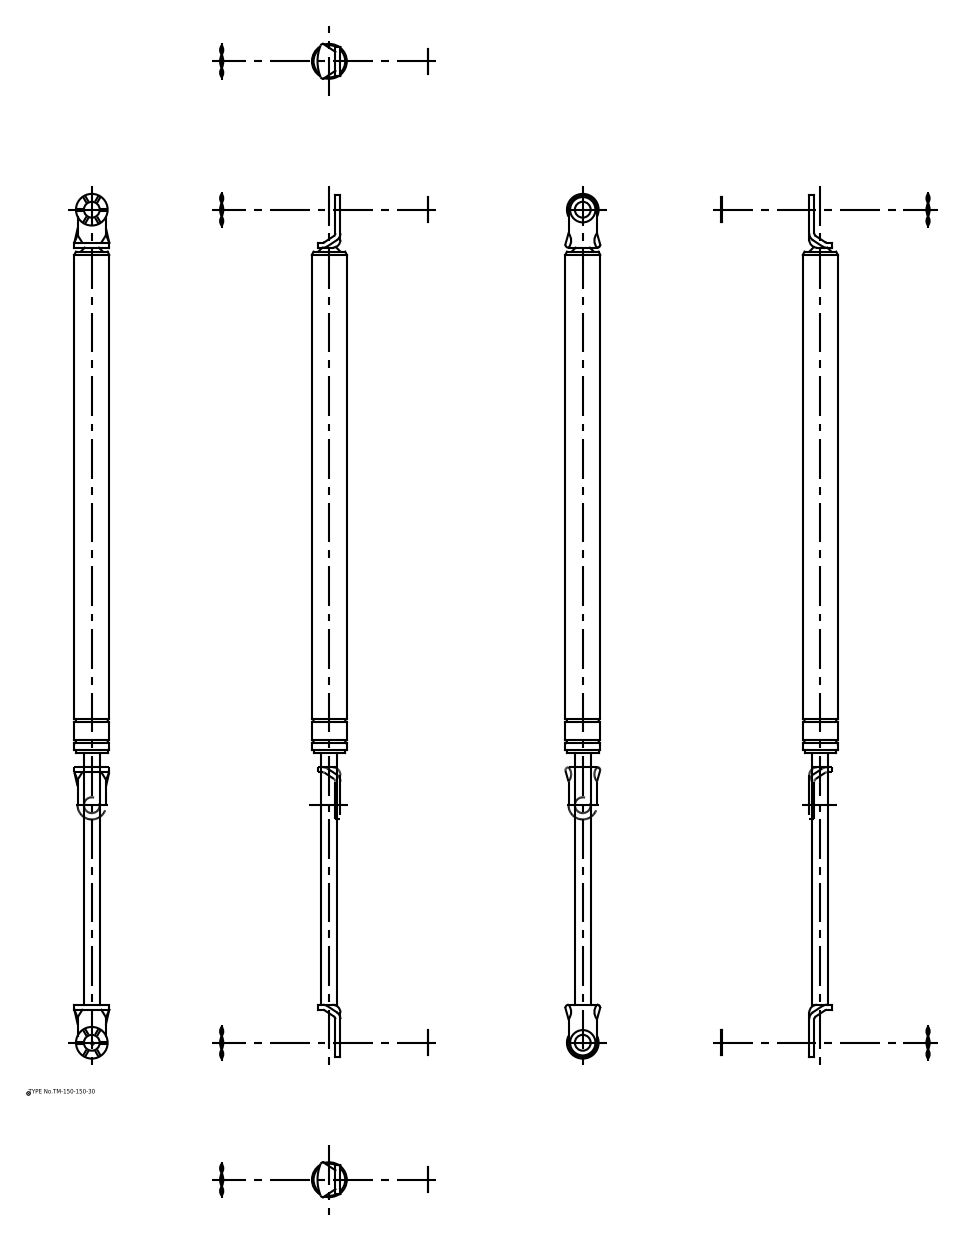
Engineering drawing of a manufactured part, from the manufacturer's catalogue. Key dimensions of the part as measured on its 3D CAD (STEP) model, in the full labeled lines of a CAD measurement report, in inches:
Part name (STEP PRODUCT): ウェーブワッシャー; ワッシャー; 本体; 本体_div
STEP written by: spGate 16.7.1 (AUTOMOTIVE_DESIGN)
Units: inches
Bodies: 6 solids, 94 faces (42 planar, 44 cylindrical, 8 other)
Overall size (bounding box): 21.496 × 0.886 × 0.886
Volume: 8.453 in³ · Surface area: 51.65 in²
Round holes (diameter × count): ⌀0.394 ×2
Round bosses / shafts (diameter × count): ⌀0.787 ×3, ⌀0.63 ×2, ⌀0.886 ×1, ⌀0.866 ×1, ⌀0.394 ×1
Partial cylindrical surfaces — rounded edges, fillets, slot ends (radius × count): R0.173 ×2, R0.197 ×2, R0.354 ×2, R1.036 ×1
Main face-to-face distances: 0.126, 0.079, 0.205, 18.945, 0.224, 0.146, 0.02, 12.685, 6.386, 19.071
Hole centre spacings: 20.709
